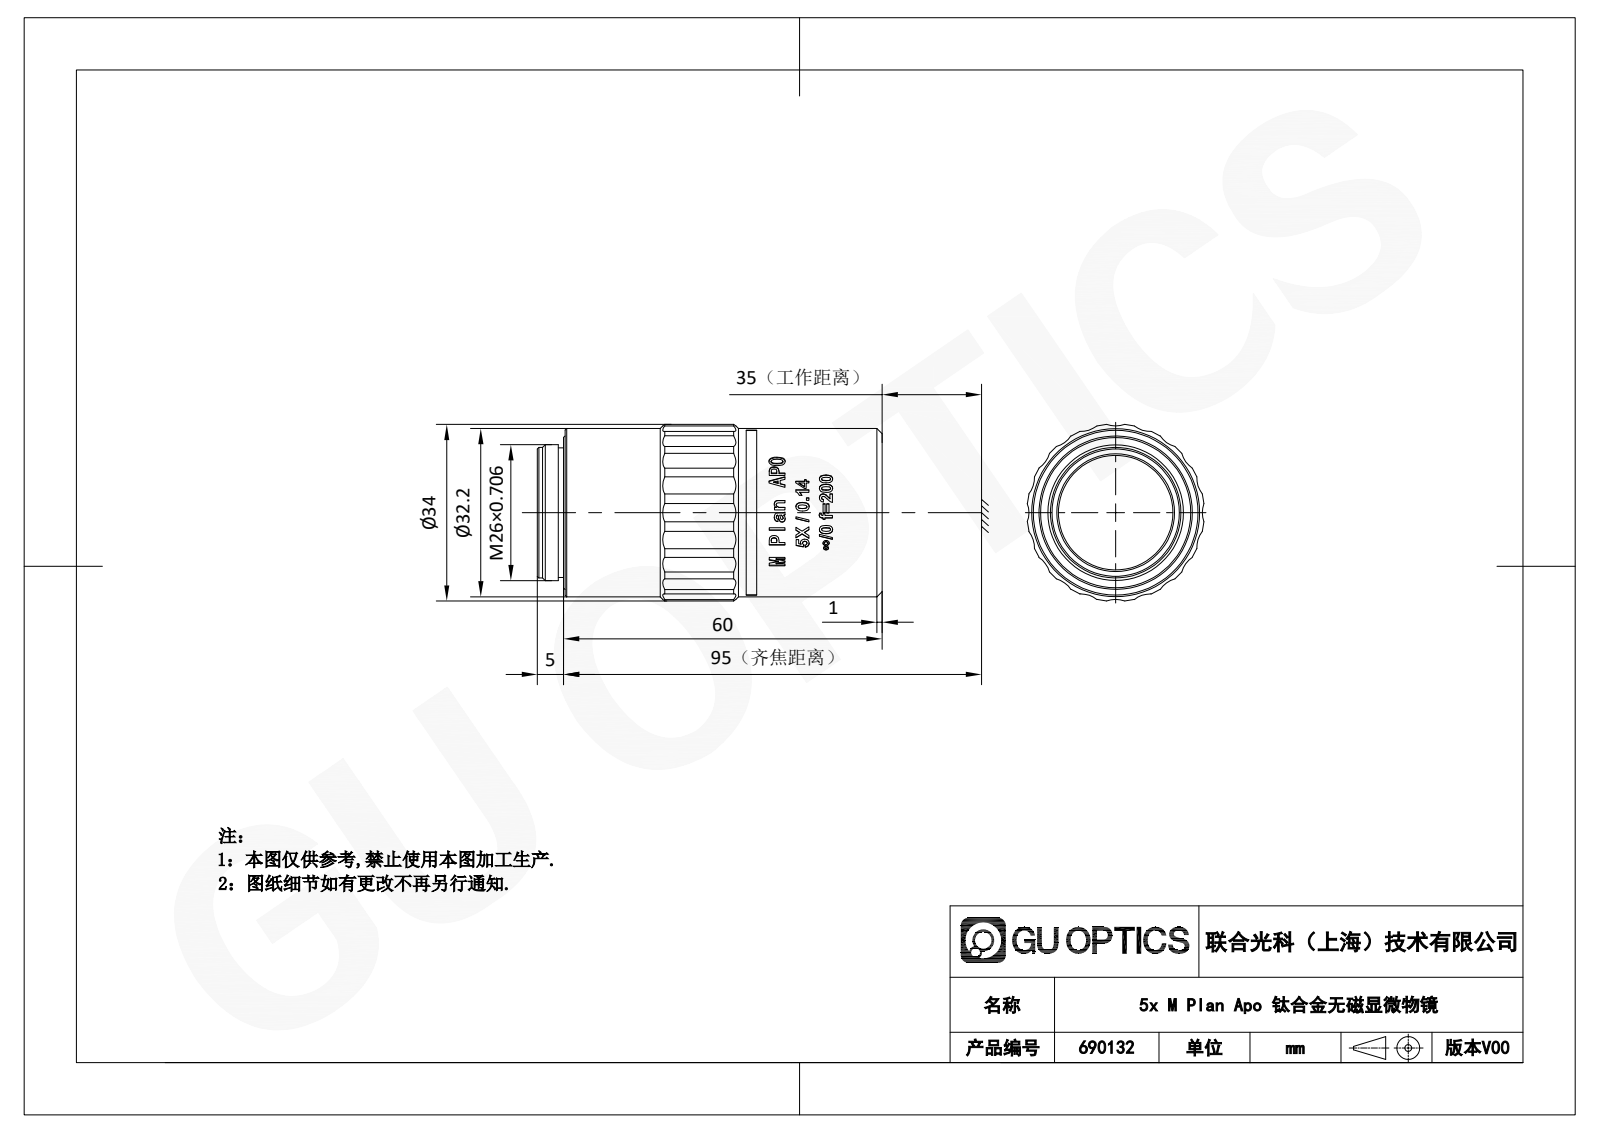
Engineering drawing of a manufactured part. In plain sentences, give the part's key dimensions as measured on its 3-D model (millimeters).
The part is named "690132". Its 3-D file was written by "SolidWorks 2020 (CONFIG_CONTROL_DESIGN)". It is 1 solid with 367 faces: 114 planar, 85 cylindrical and 168 other. Overall it measures 65 by 33.82 by 33.82 millimeters. Its volume is 50 519 cubic millimeters and its surface area 8 604 square millimeters. Round holes: 1 of diameter 20, 1 of diameter 22. Round bosses or shafts: 1 of diameter 32.2, 1 of diameter 32, 1 of diameter 26, 1 of diameter 25, 1 of diameter 24.8. Partial cylindrical surfaces (rounded edges, fillets, slot ends): 20 of radius 5, 1 of radius 15.9, 1 of radius 17. The main face-to-face distances are 61.3, 1.3, 60, 1.6, 59.7, 3.7, 5, 5.3, 65, 4.
